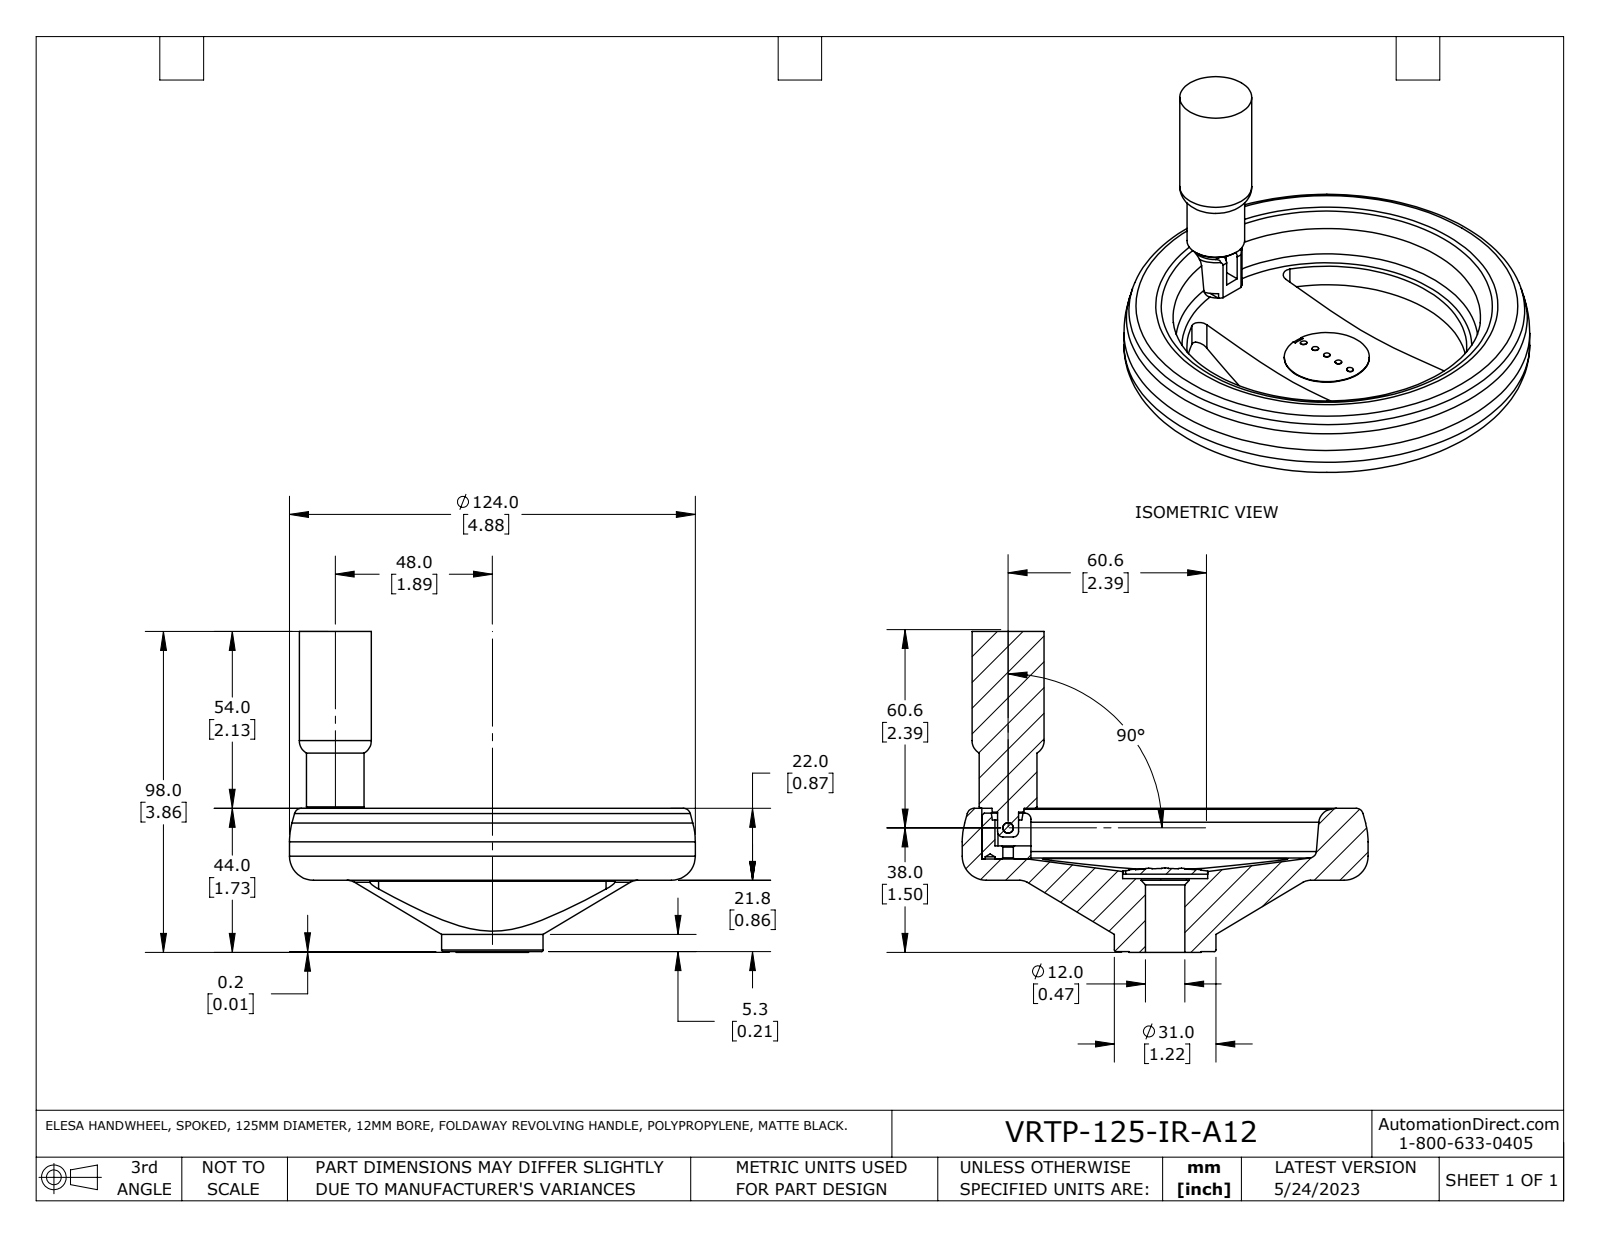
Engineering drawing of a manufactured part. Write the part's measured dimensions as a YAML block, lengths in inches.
part_name: "VRTP-125-IR-A12"
step_written_by: "SolidWorks 2021 (AUTOMOTIVE_DESIGN)"
units: inches
bodies: {solids: 4, faces: 100, planar: 34, cylindrical: 35, other: 31}
overall_size: [4.882, 4.882, 3.858]
volume: 10.87
surface_area: 65.69
round_holes:
  - {diameter: 0.079, count: 5}
  - {diameter: 0.118, count: 1}
  - {diameter: 0.126, count: 1}
  - {diameter: 0.128, count: 1}
  - {diameter: 0.472, count: 1}
  - {diameter: 0.63, count: 1}
  - {diameter: 1.024, count: 1}
round_bosses_or_shafts:
  - {diameter: 0.866, count: 2}
  - {diameter: 4.882, count: 1}
  - {diameter: 1.22, count: 1}
  - {diameter: 0.693, count: 1}
  - {diameter: 0.252, count: 1}
partial_cylinders:
  - {radius: 0.109, count: 4}
  - {radius: 0.036, count: 2}
  - {radius: 0.063, count: 2}
  - {radius: 0.072, count: 1}
  - {radius: 0.475, count: 1}
  - {radius: 1.683, count: 1}
face_to_face_distances: [0.866, 1.343, 0.02, 0.846, 0.073, 0.053, 0.793, 2.992, 2.972, 2.919]
hole_center_spacings: [0.197, 0.217, 0.394, 1.693, 1.89, 1.909, 2.087, 2.106]
